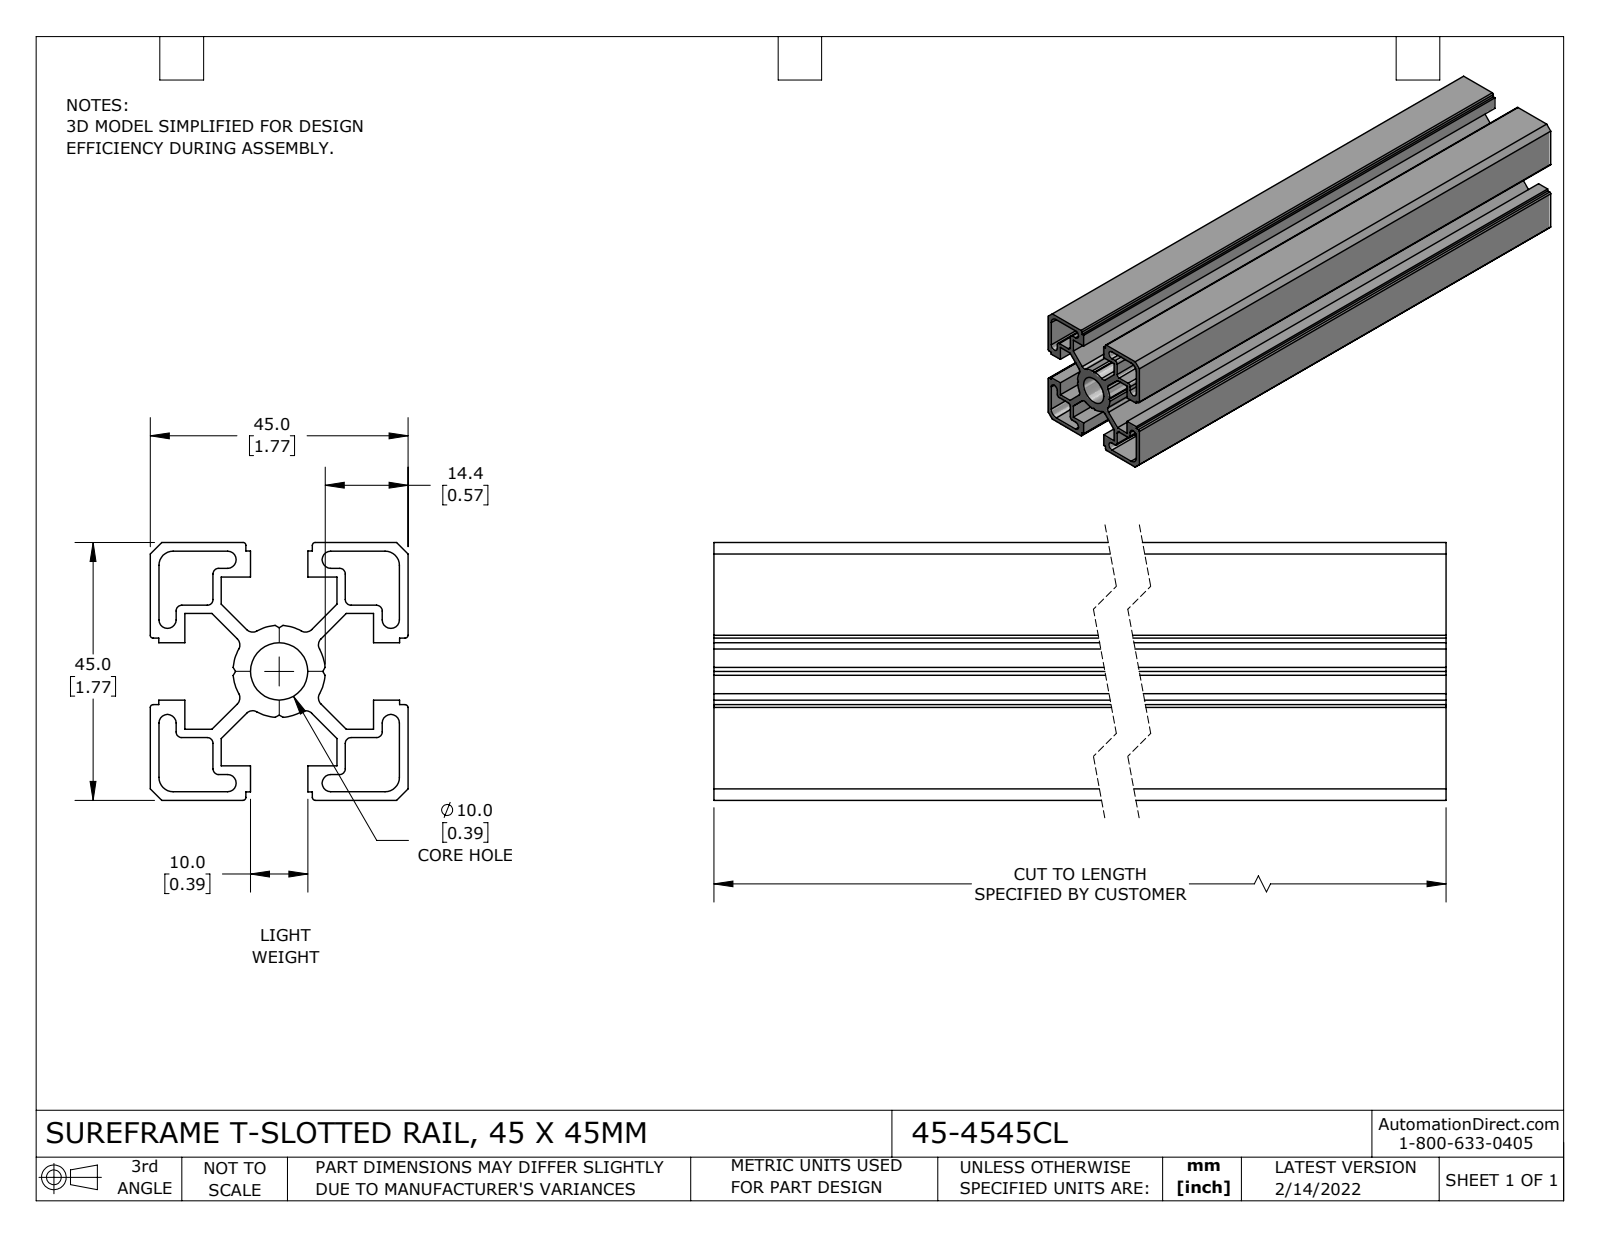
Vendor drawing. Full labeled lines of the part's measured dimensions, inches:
Part name (STEP PRODUCT): 45-4545CL
STEP written by: SolidWorks 2021 (CONFIG_CONTROL_DESIGN)
Units: inches
Bodies: 1 solid, 146 faces (94 planar, 52 cylindrical, 0 other)
Overall size (bounding box): 8 × 1.772 × 1.772
Volume: 7.313 in³ · Surface area: 186.8 in²
Round holes (diameter × count): ⌀0.394 ×1
Partial cylindrical surfaces — rounded edges, fillets, slot ends (radius × count): R0.059 ×16, R0.039 ×12, R0.02 ×8, R0.098 ×4, R0.317 ×1
Main face-to-face distances: 0.059, 1.713, 1.772, 0.237, 1.534, 0.178, 1.475, 1.654, 0.488, 1.283
